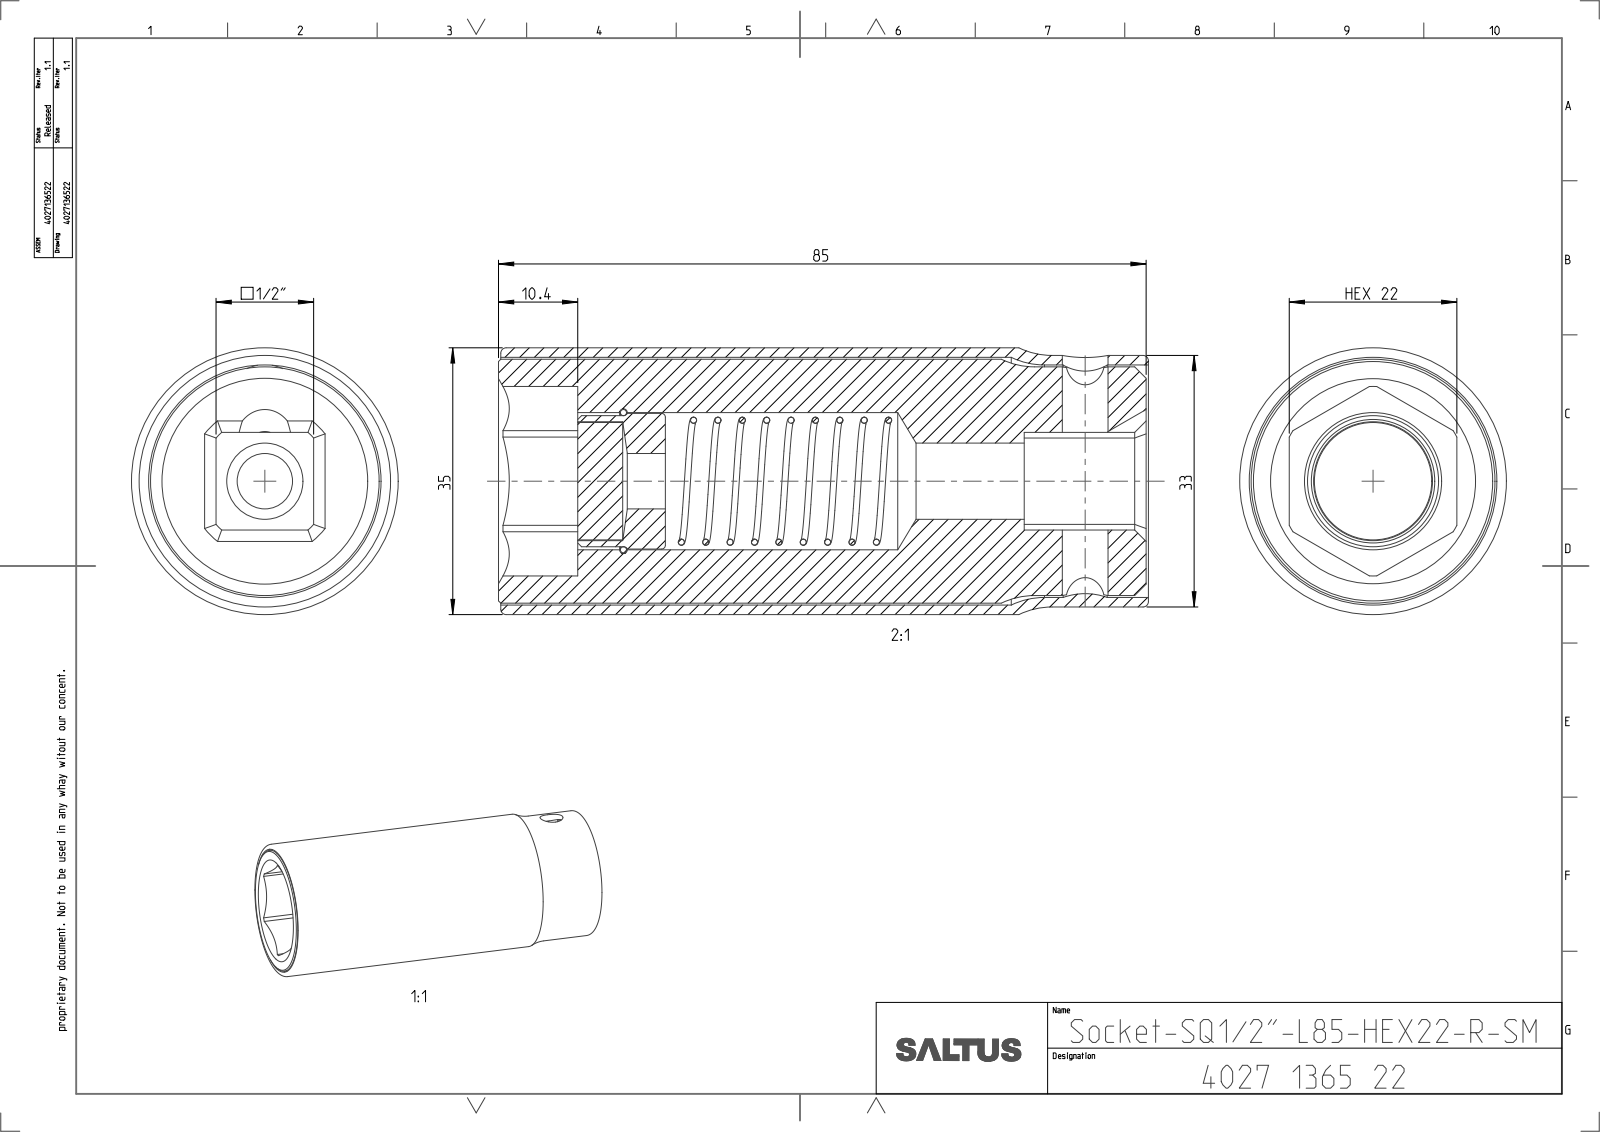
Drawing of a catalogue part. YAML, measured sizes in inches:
part_name: "4027134022; 4027299395; 4027136522_ASM"
step_written_by: "CREO PARAMETRIC BY PTC INC, 2022414 (CONFIG_CONTROL_DESIGN)"
units: inches
bodies: {solids: 6, faces: 122, planar: 28, cylindrical: 49, other: 45}
overall_size: [3.358, 1.378, 1.378]
volume: 3.675
surface_area: 55.42
round_holes:
  - {diameter: 0.236, count: 1}
  - {diameter: 0.286, count: 1}
  - {diameter: 0.394, count: 1}
  - {diameter: 0.614, count: 1}
  - {diameter: 0.709, count: 1}
  - {diameter: 1.201, count: 1}
  - {diameter: 1.28, count: 1}
round_bosses_or_shafts:
  - {diameter: 1.378, count: 1}
  - {diameter: 1.299, count: 1}
  - {diameter: 1.26, count: 1}
  - {diameter: 1.181, count: 1}
  - {diameter: 0.701, count: 1}
  - {diameter: 0.677, count: 1}
  - {diameter: 0.606, count: 1}
partial_cylinders:
  - {radius: 0.157, count: 1}
  - {radius: 0.337, count: 1}
  - {radius: 0.489, count: 1}
face_to_face_distances: [0.866, 2.937, 0.505, 3.346, 2.705, 0.642, 0.181, 0.685, 0.409, 0.232]
